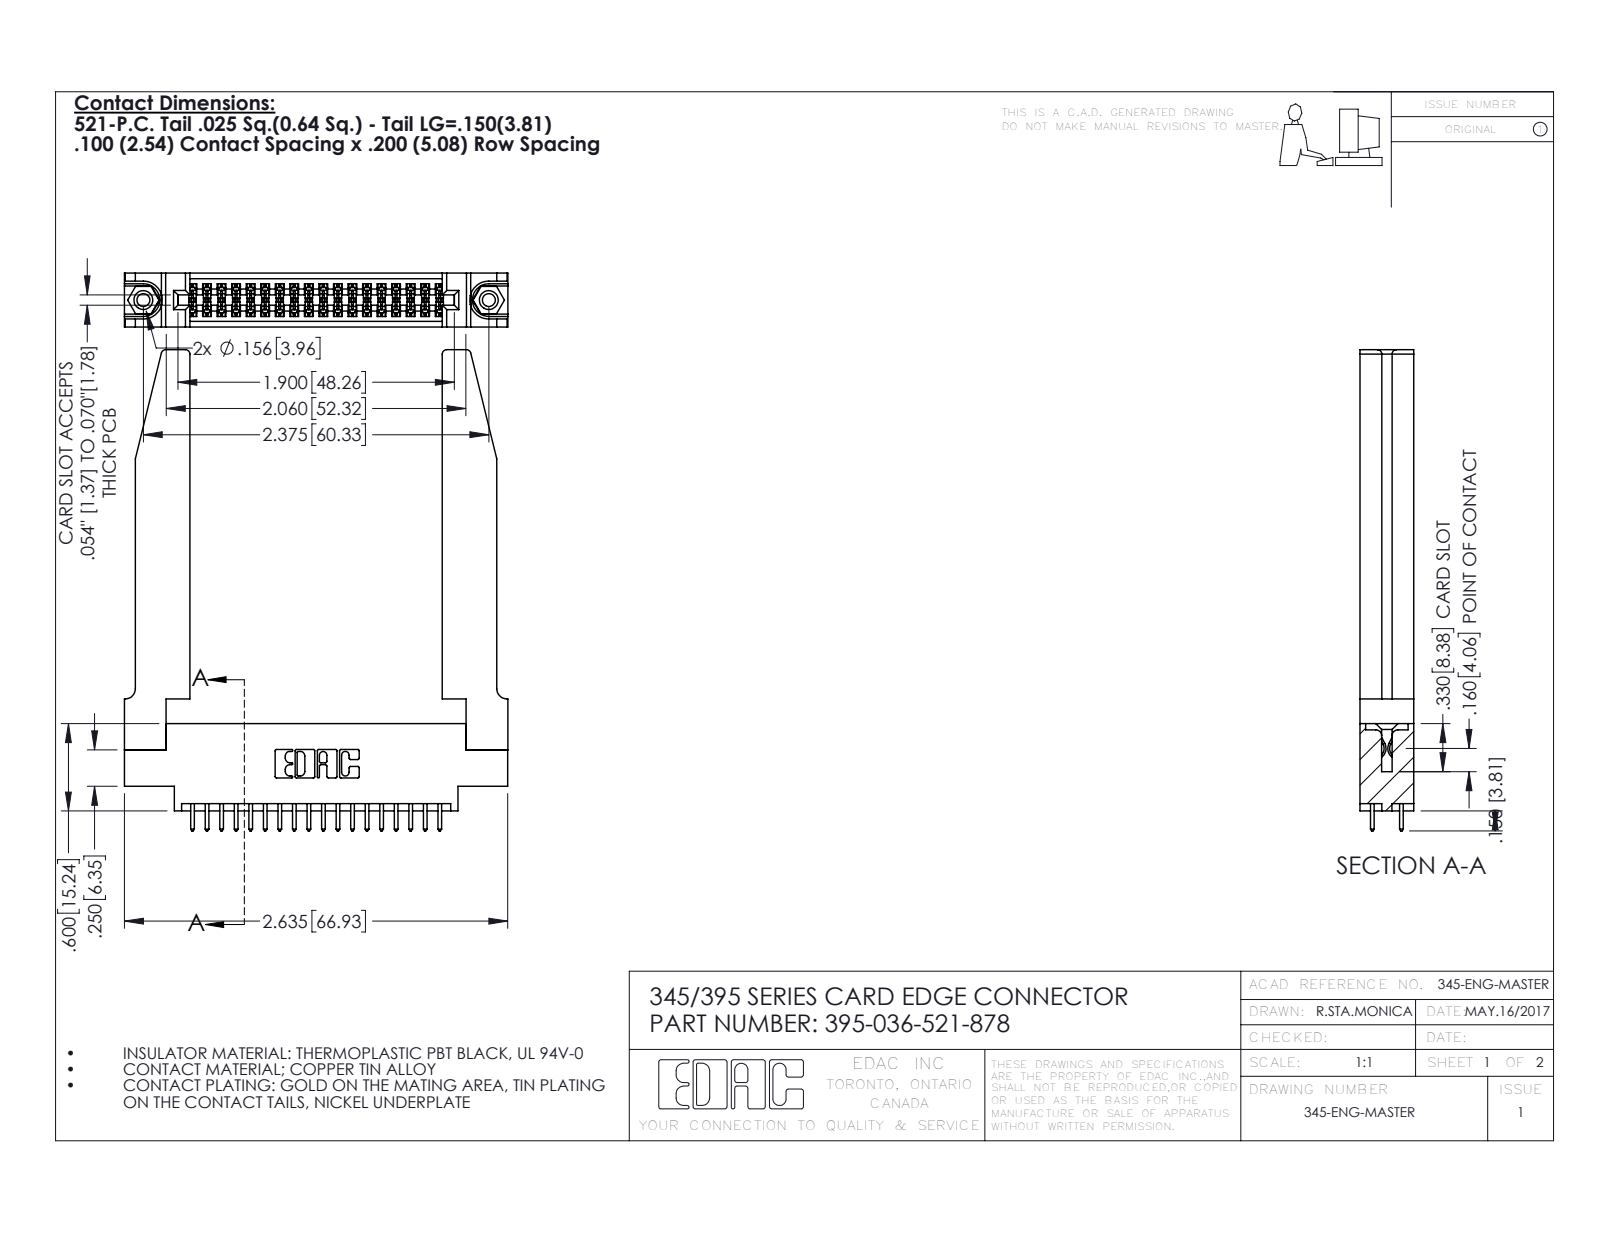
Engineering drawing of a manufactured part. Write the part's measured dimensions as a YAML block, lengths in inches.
part_name: "345 Part_0.170 Offset - 0.156 Dia-TH; 395-036-521-878; 345-292-001_345-293-121; 345-220-078_345-220-078 (+1 more)"
step_written_by: "SolidWorks 2016 (CONFIG_CONTROL_DESIGN)"
units: inches
bodies: {solids: 41, faces: 2164, planar: 1414, cylindrical: 698, other: 52}
overall_size: [3.307, 2.636, 0.37]
volume: 0.85
surface_area: 24.05
round_holes:
  - {diameter: 0.089, count: 2}
  - {diameter: 0.125, count: 2}
  - {diameter: 0.156, count: 2}
  - {diameter: 0.064, count: 1}
round_bosses_or_shafts:
  - {diameter: 0.155, count: 2}
partial_cylinders:
  - {radius: 0.006, count: 54}
  - {radius: 0.01, count: 36}
  - {radius: 0.01, count: 22}
  - {radius: 0.03, count: 8}
  - {radius: 0.007, count: 6}
  - {radius: 0.031, count: 6}
  - {radius: 0.026, count: 3}
  - {radius: 0.014, count: 2}
face_to_face_distances: [0.37, 0.072, 0.298, 0.098, 0.272, 0.025, 0.2, 0.15, 0.148, 0.225]
hole_center_spacings: [0.27, 2.141, 2.375]
